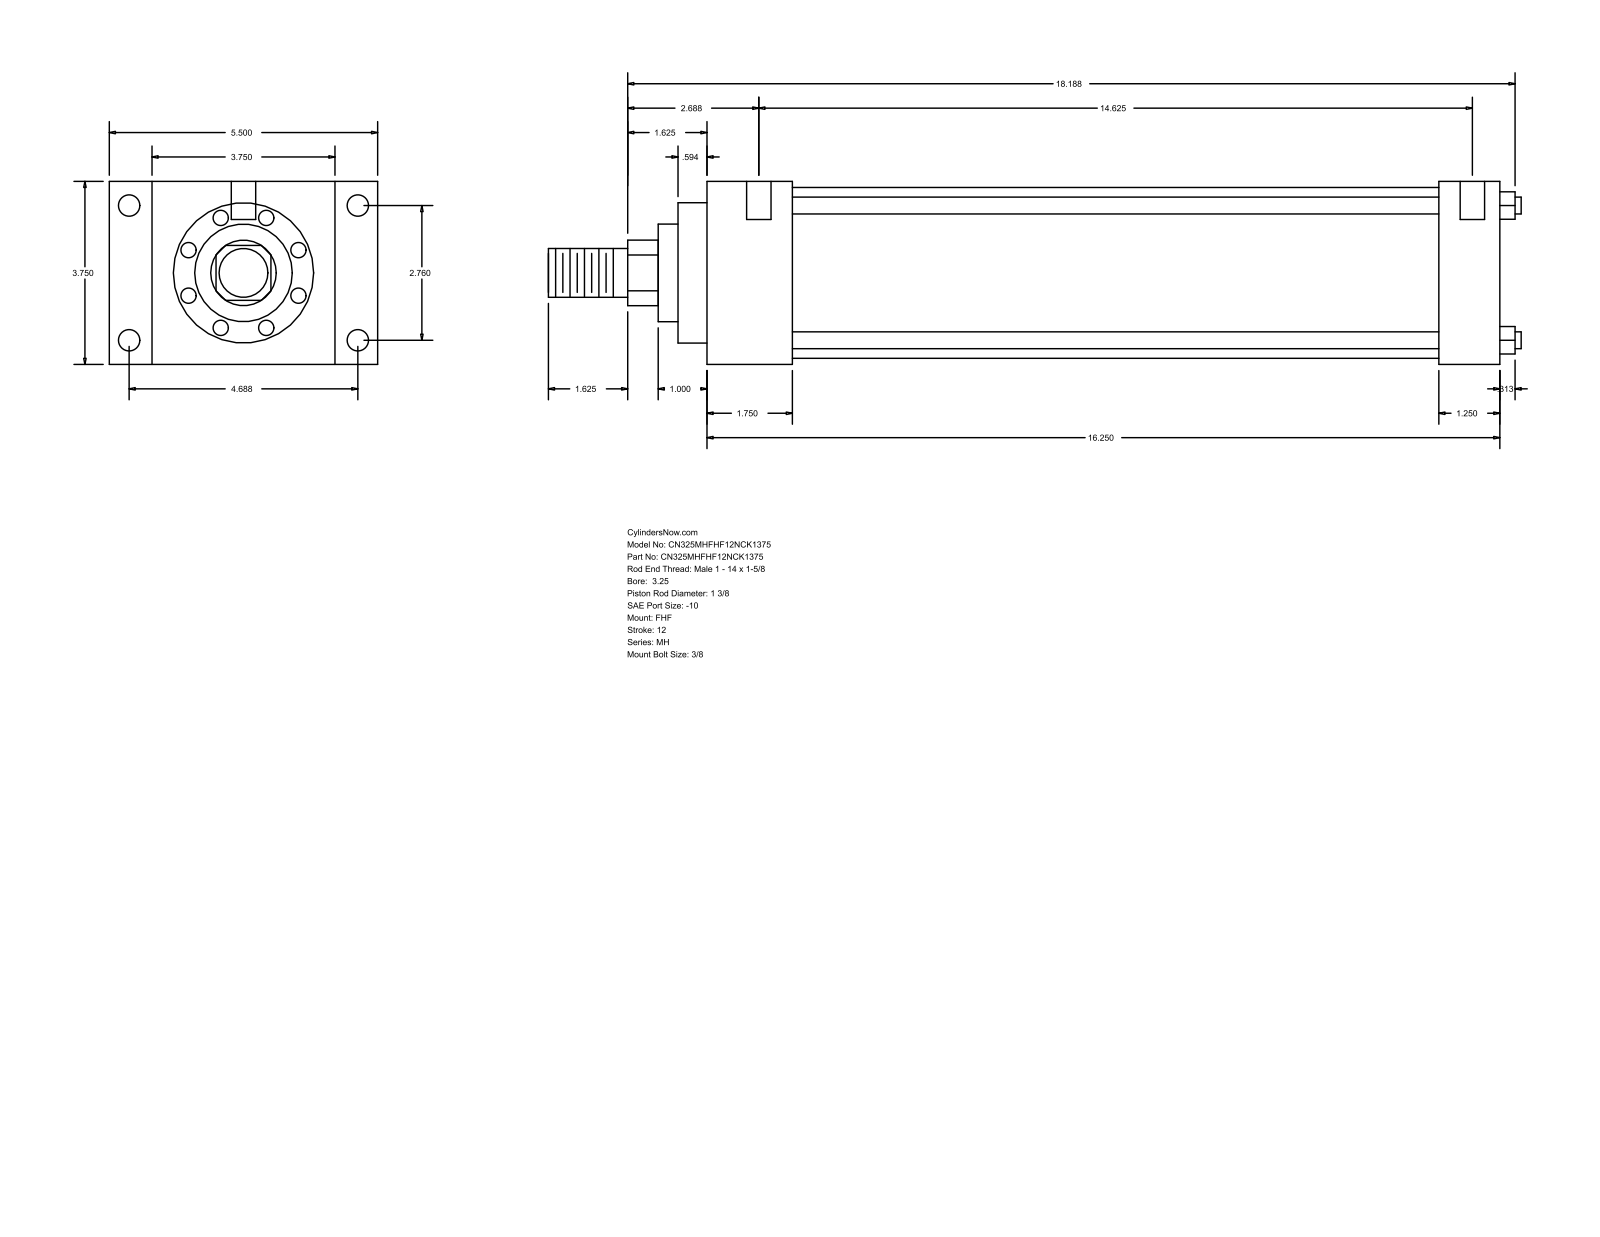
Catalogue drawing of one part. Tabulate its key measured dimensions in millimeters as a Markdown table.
| quantity | value |
| --- | --- |
| part name | MH_FHF__0325_1.375 |
| STEP written by | GSSL Pune (CONFIG_CONTROL_DESIGN) |
| units | millimeters |
| bodies | 0 solids, 90 faces (61 planar, 29 cylindrical, 0 other) |
| overall size | 506.41 × 139.7 × 95.25 |
| round holes (diameter × count) | 5.56 × 4, 11.13 × 4, 12.7 × 2 |
| round bosses / shafts (diameter × count) | 8.76 × 4, 88.9 × 1, 73.03 × 1, 50.8 × 1, 34.92 × 1, 25.4 × 1 |
| partial cylindrical surfaces (radius × count) | 17.06 × 1 |
| main face-to-face distances | 95.24, 412.75, 44.45, 368.3, 22.23, 117.47, 139.7, 381, 336.55, 31.75 |
| hole center spacings | 70.1, 119.06, 138.16, 377.83, 1.59, 4.76, 371.48, 373.07 |
